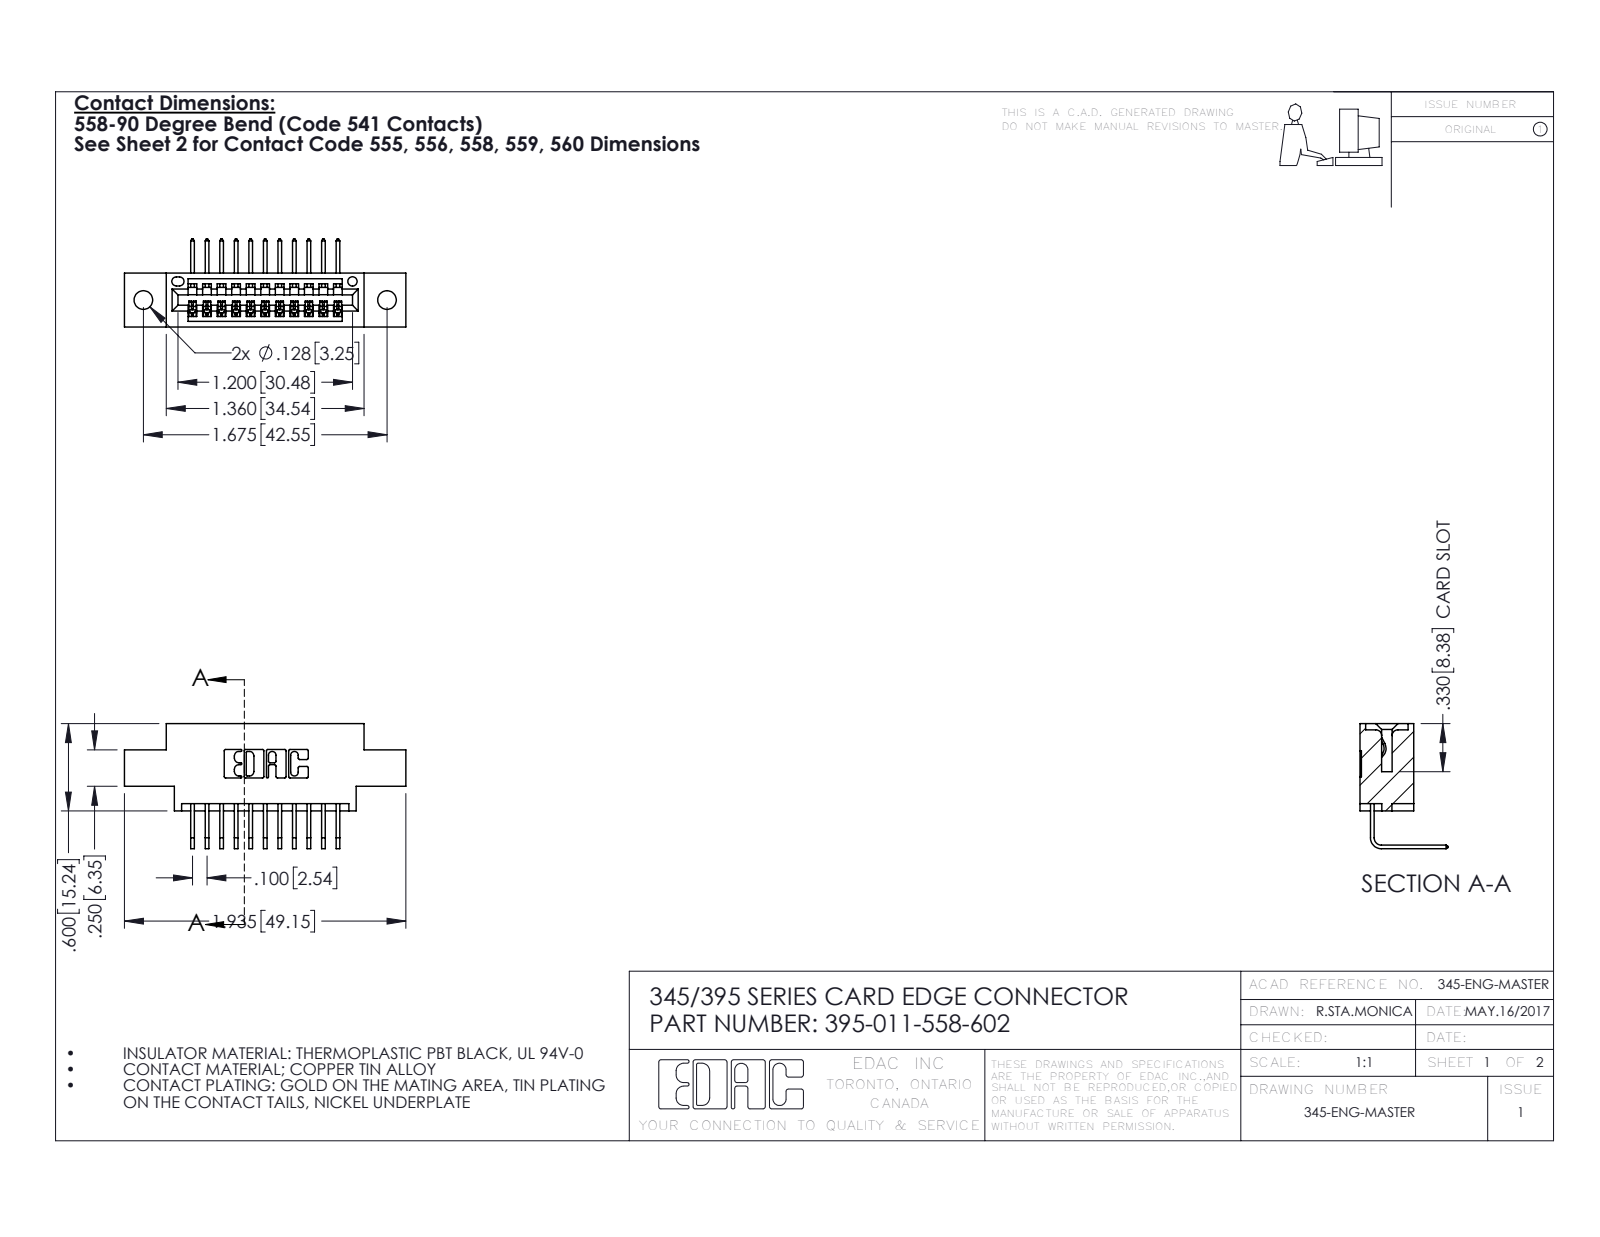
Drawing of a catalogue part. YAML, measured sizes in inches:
part_name: "395-011-558-602; 345 Part_0.170 Offset - 0.128 Dia; 345-292-001_558 Tail - 2"
step_written_by: "SolidWorks 2016 (CONFIG_CONTROL_DESIGN)"
units: inches
bodies: {solids: 12, faces: 790, planar: 546, cylindrical: 244, other: 0}
overall_size: [1.935, 0.859, 0.605]
volume: 0.262
surface_area: 8.315
round_holes:
  - {diameter: 0.128, count: 2}
  - {diameter: 0.064, count: 1}
partial_cylinders:
  - {radius: 0.006, count: 22}
  - {radius: 0.01, count: 22}
  - {radius: 0.007, count: 6}
  - {radius: 0.031, count: 6}
  - {radius: 0.026, count: 3}
  - {radius: 0.031, count: 2}
  - {radius: 0.04, count: 2}
  - {radius: 0.014, count: 1}
face_to_face_distances: [0.37, 0.072, 0.298, 0.2, 0.098, 0.272, 0.025, 0.1, 0.6, 0.225]
hole_center_spacings: [0.27, 1.443, 1.675]
